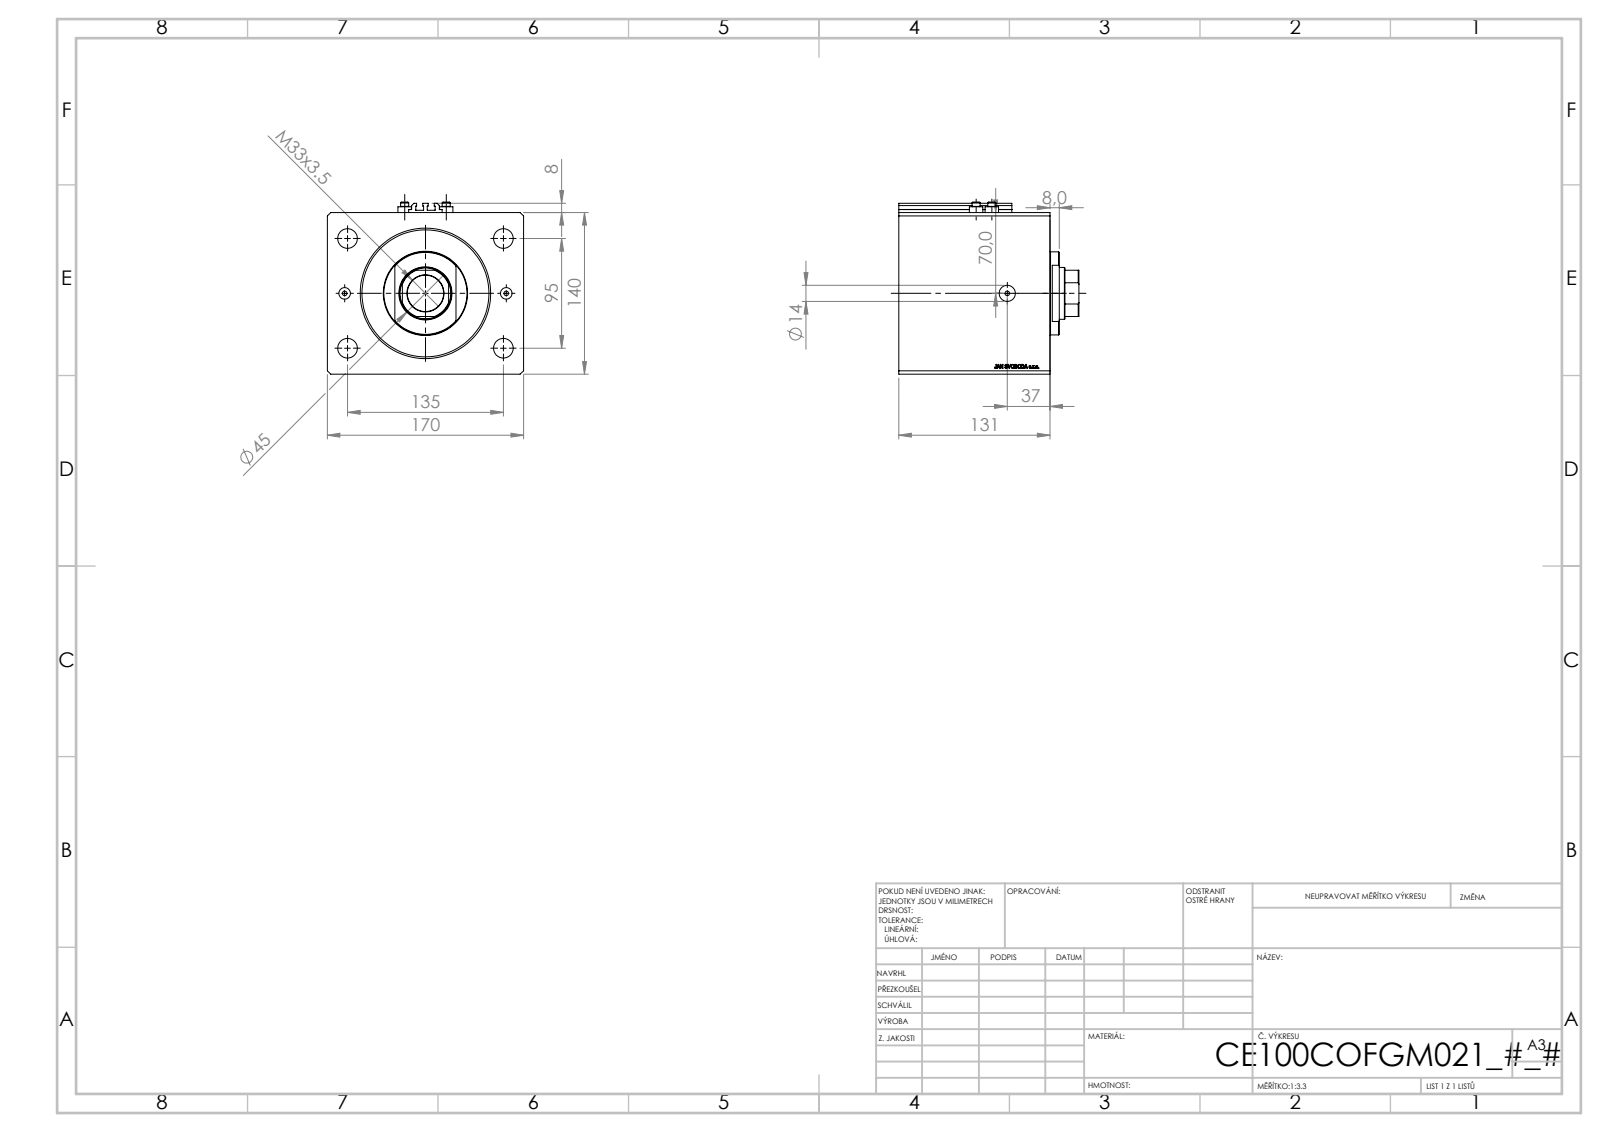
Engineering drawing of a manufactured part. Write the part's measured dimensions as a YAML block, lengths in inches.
part_name: "V250CE_C_VCP; V250CE_VC_C; V250CE_C_Body; ALLEN BOLT V250CE"
step_written_by: "SolidWorks 2019 (CONFIG_CONTROL_DESIGN)"
units: inches
bodies: {solids: 8, faces: 1034, planar: 504, cylindrical: 86, other: 444}
overall_size: [6.693, 6.142, 5.866]
volume: 176.1
surface_area: 437.8
round_holes:
  - {diameter: 0.157, count: 8}
  - {diameter: 0.669, count: 4}
  - {diameter: 0.394, count: 2}
  - {diameter: 0.551, count: 2}
  - {diameter: 1.24, count: 1}
  - {diameter: 1.772, count: 1}
  - {diameter: 3.937, count: 1}
  - {diameter: 4.449, count: 1}
round_bosses_or_shafts:
  - {diameter: 0.457, count: 4}
  - {diameter: 0.276, count: 4}
  - {diameter: 2.835, count: 1}
partial_cylinders:
  - {radius: 0.008, count: 10}
  - {radius: 0.866, count: 1}
face_to_face_distances: [5.512, 5.157, 6.693, 1.138, 4.02, 0.984, 4.173, 3.035, 1.811, 3.346]
hole_center_spacings: [1.873, 3.25, 5.727, 0.535, 1.417, 1.515, 2.756, 3.74]
